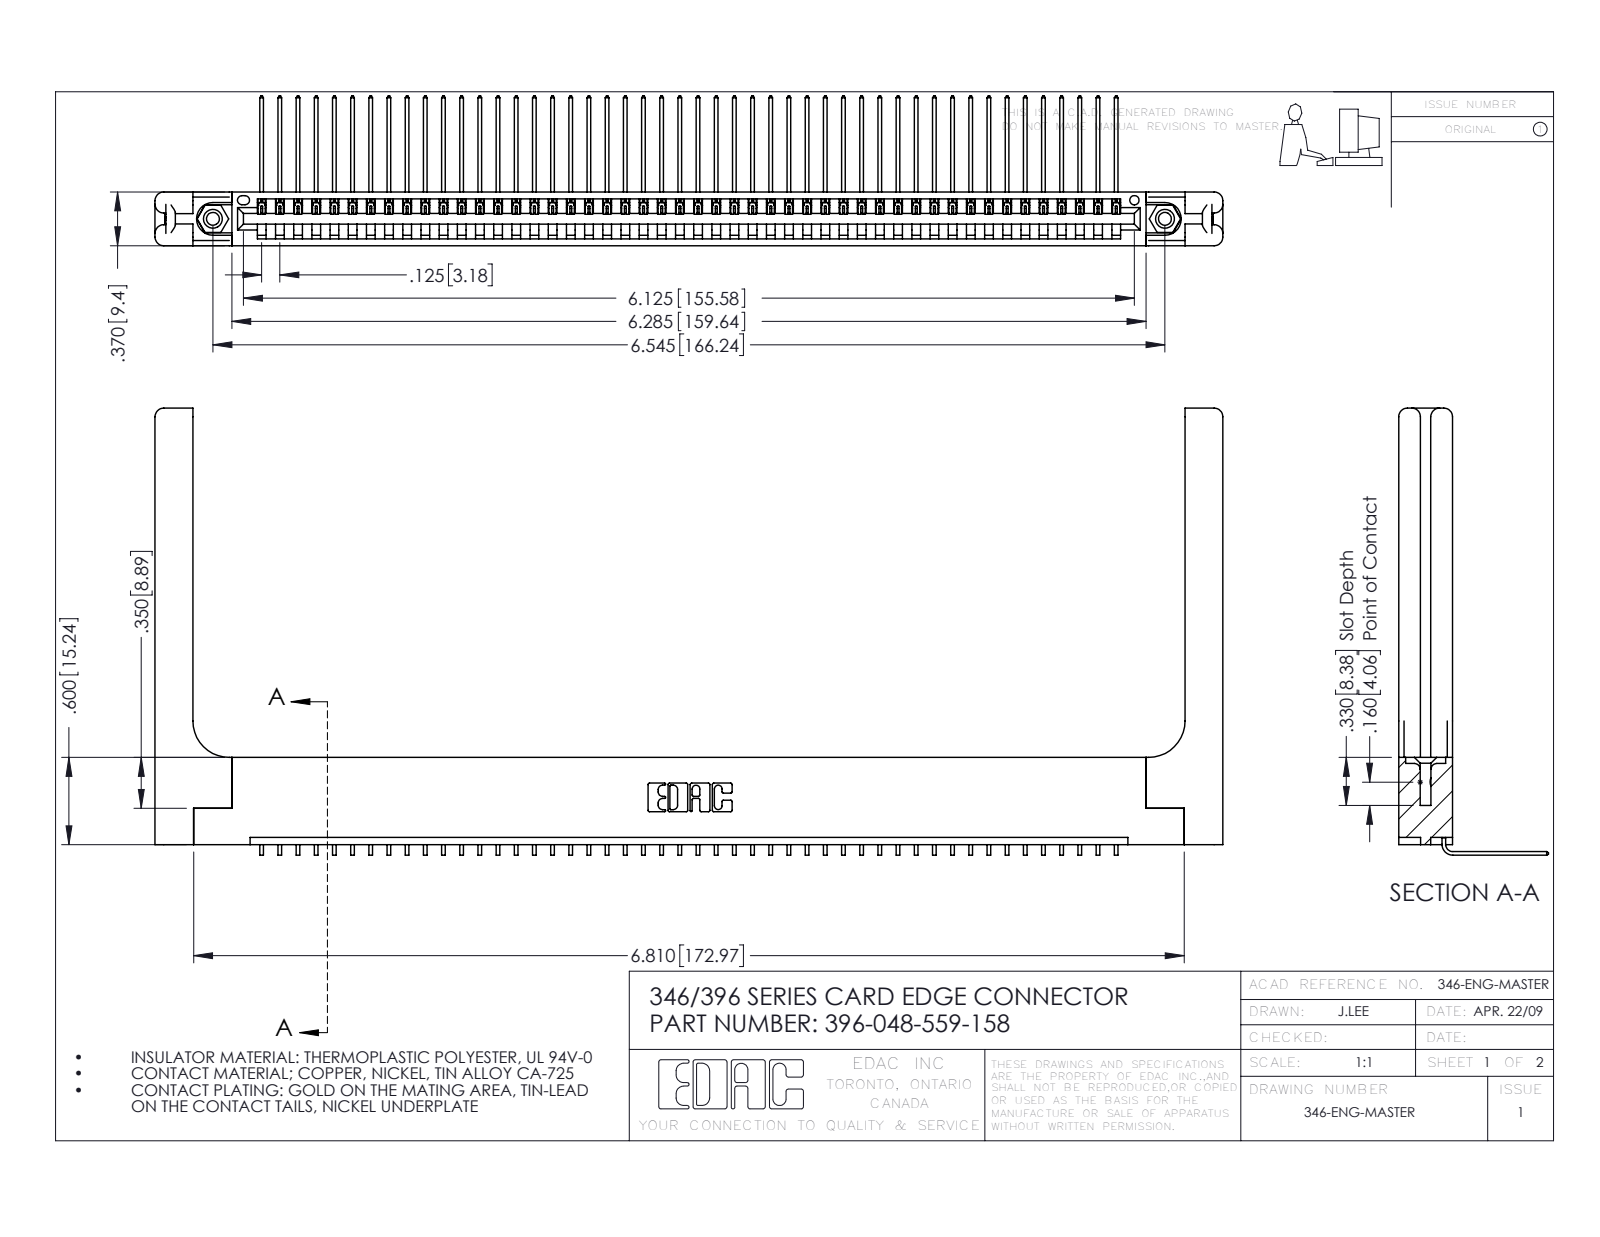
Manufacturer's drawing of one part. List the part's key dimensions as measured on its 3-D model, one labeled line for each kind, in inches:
Part name (STEP PRODUCT): 396-048-559-158; 345-292-001_558 559 Tail - 1; 346-220-058_345-220-058; 346 Part_Flush Mounting Lugs - 0.156 Dia-TH (+1 more)
STEP written by: SolidWorks 2016 (CONFIG_CONTROL_DESIGN)
Units: inches
Bodies: 53 solids, 3258 faces (2240 planar, 958 cylindrical, 60 other)
Overall size (bounding box): 7.341 × 3.073 × 1.03
Volume: 1.56 in³ · Surface area: 44.56 in²
Round holes (diameter × count): ⌀0.089 ×2, ⌀0.125 ×2, ⌀0.156 ×2, ⌀0.064 ×1
Round bosses / shafts (diameter × count): ⌀0.155 ×2
Partial cylindrical surfaces — rounded edges, fillets, slot ends (radius × count): R0.006 ×96, R0.01 ×22, R0.06 ×16, R0.007 ×6, R0.031 ×6, R0.026 ×3, R0.03 ×2, R0.031 ×2
Main face-to-face distances: 0.37, 0.048, 0.322, 0.072, 0.148, 0.15, 0.025, 0.25, 0.298, 0.222
Hole centre spacings: 0.246, 6.336, 6.545
